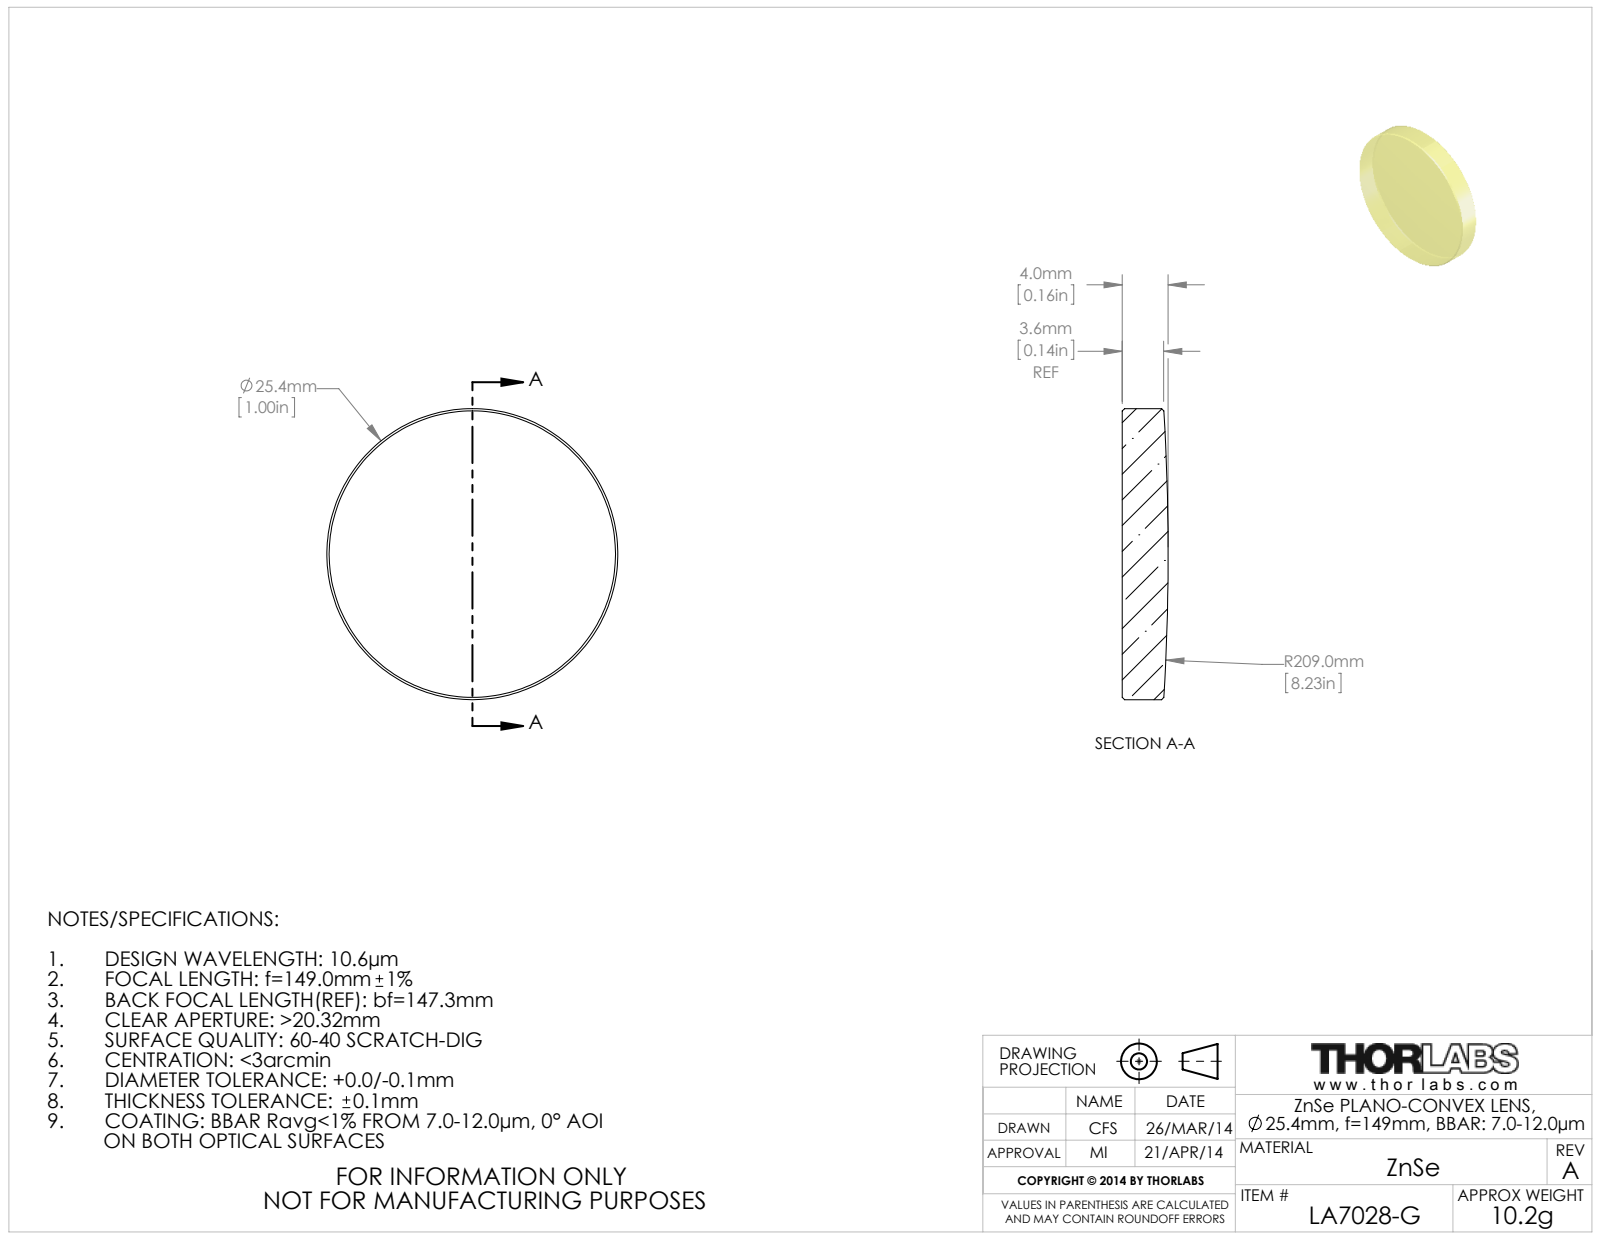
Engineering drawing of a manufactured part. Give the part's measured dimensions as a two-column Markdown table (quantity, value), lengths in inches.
| quantity | value |
| --- | --- |
| part name | TTN023916-E0W |
| STEP written by | SolidWorks 2012 (CONFIG_CONTROL_DESIGN) |
| units | inches |
| bodies | 1 solid, 9 faces (1 planar, 2 cylindrical, 6 other) |
| overall size | 1 × 1 × 0.157 |
| volume | 0.118 in³ |
| surface area | 1.991 in² |
| round bosses / shafts (diameter × count) | 1 × 1 |
